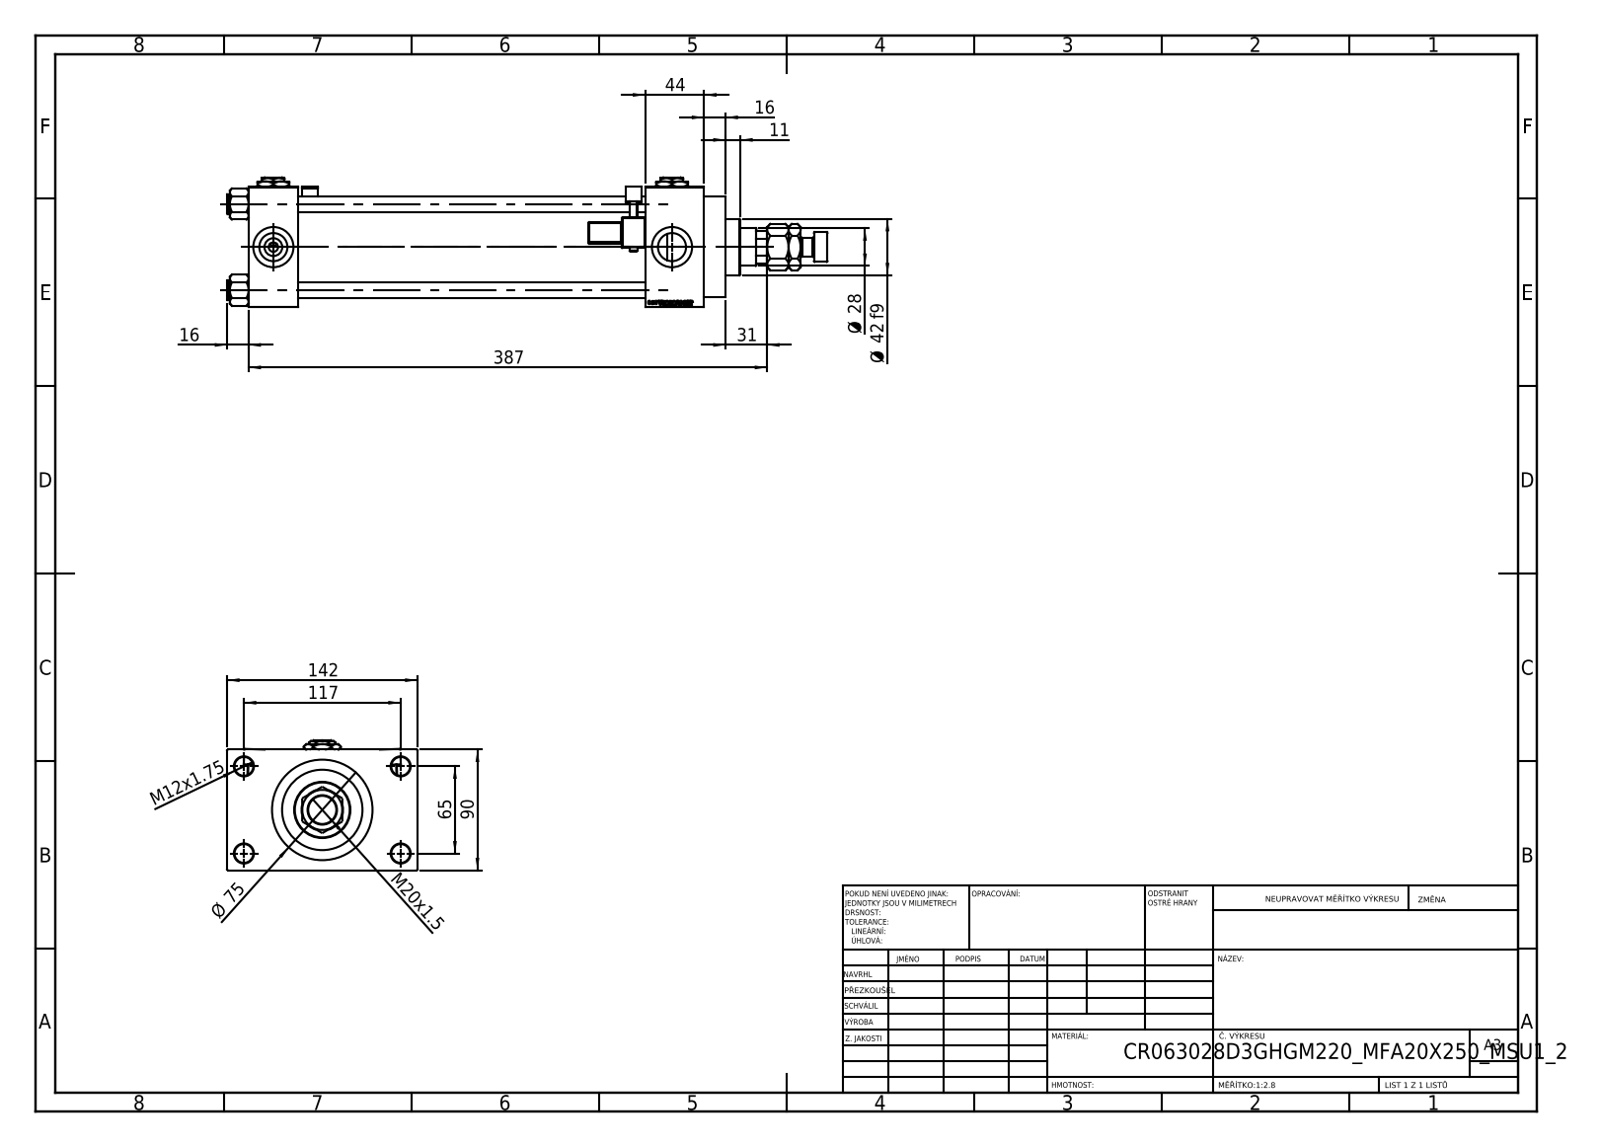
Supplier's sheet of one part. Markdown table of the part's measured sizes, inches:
| quantity | value |
| --- | --- |
| part name | V215CR_VCP_D; Zatka_pro_OIL_PORT; V215_VC_A; NUT_M5_D (+4 more) |
| STEP written by | SolidWorks 2019 (CONFIG_CONTROL_DESIGN) |
| units | inches |
| bodies | 16 solids, 1410 faces (619 planar, 163 cylindrical, 628 other) |
| overall size | 17.638 × 5.591 × 3.819 |
| volume | 91.23 in³ |
| surface area | 547.9 in² |
| round holes (diameter × count) | 0.472 × 4, 0.551 × 4, 0.825 × 4, 1.181 × 4, 0.276 × 3, 0.728 × 1, 1.102 × 1, 1.22 × 1, 1.969 × 1, 2.362 × 1, 2.48 × 1 |
| round bosses / shafts (diameter × count) | 0.591 × 4, 0.236 × 2, 2.953 × 1, 2.717 × 1, 1.654 × 1, 0.866 × 1, 0.551 × 1 |
| partial cylindrical surfaces (radius × count) | 0.02 × 48, 0.039 × 2, 0.098 × 2, 0.157 × 2, 0.531 × 1 |
| main face-to-face distances | 3.543, 10.197, 1.457, 11.654, 13.386, 11.929, 1.732, 1.024, 4.567, 14.016 |
| hole center spacings | 1.037, 1.79, 2.531, 2.635, 2.748, 3.569, 4.383, 2.559 |
